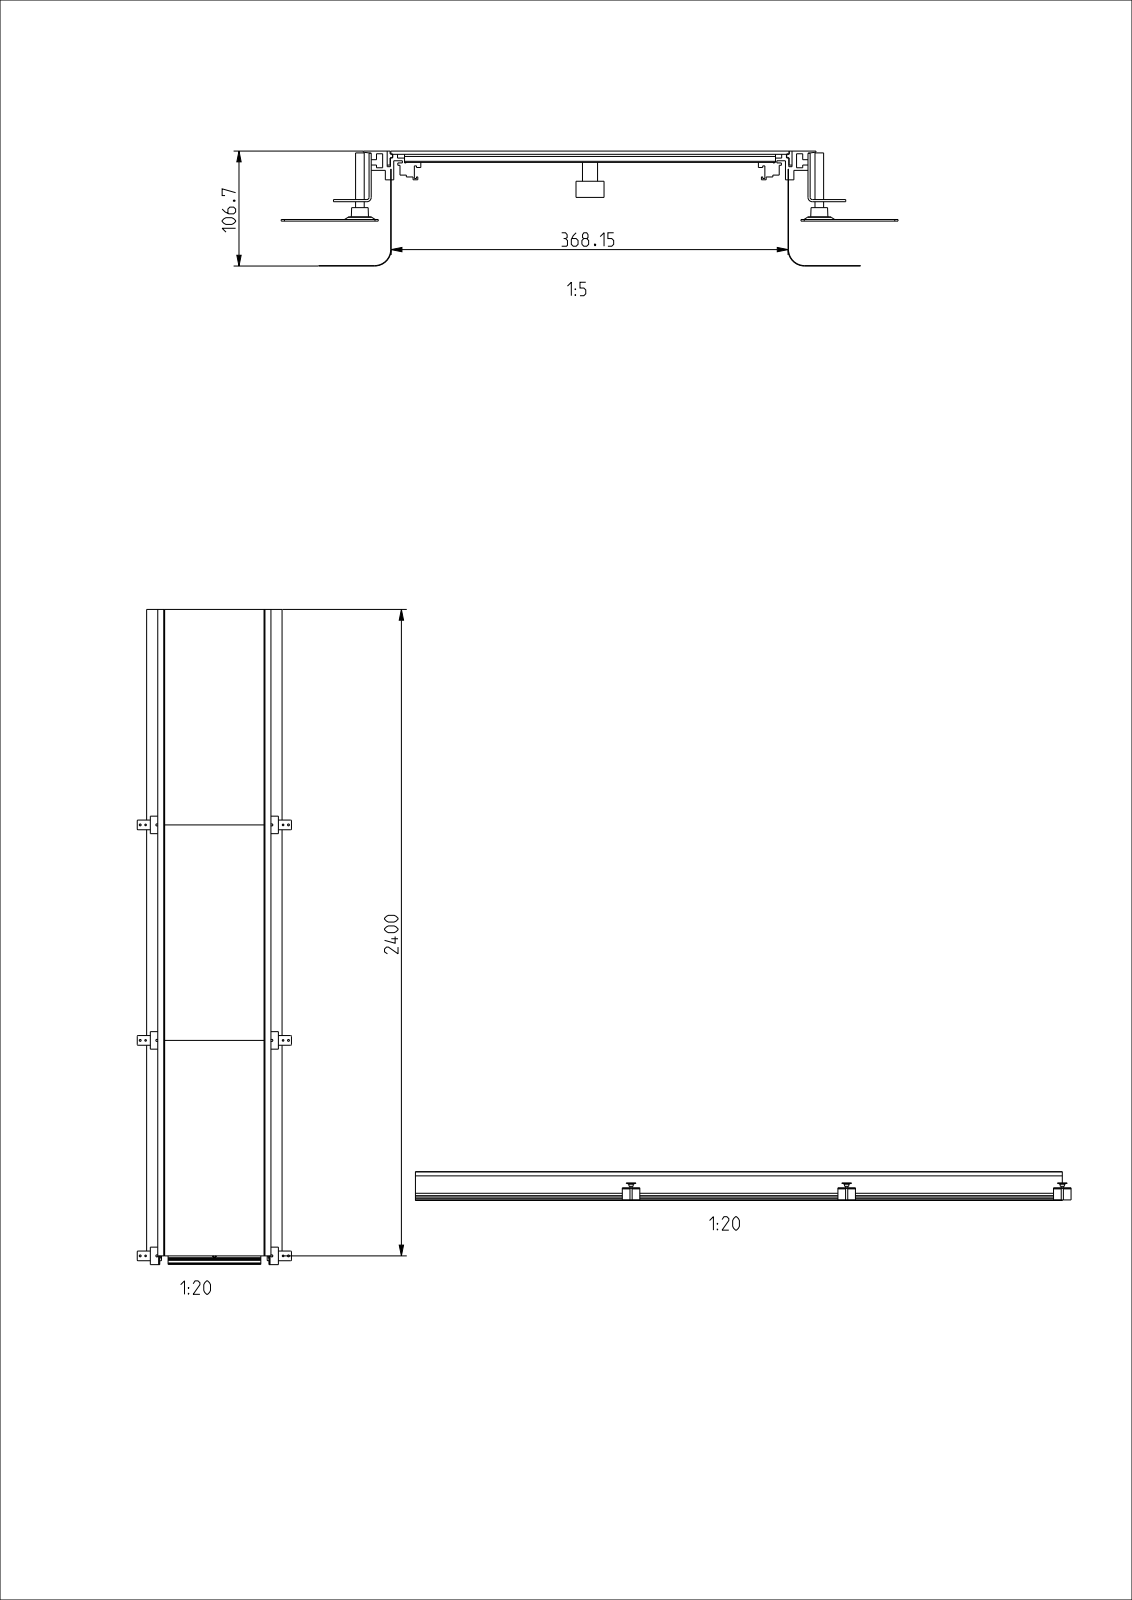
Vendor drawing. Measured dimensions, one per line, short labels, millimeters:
name: U05644KUN; U05650KUN; U05994KUN; U05647KUN (+8 more)
written by: CREO PARAMETRIC BY PTC INC, 2020281 (AUTOMOTIVE_DESIGN)
unit: mm
bodies: 62 solids, 1026 faces (600 planar, 354 cylindrical, 72 other)
size: 2432.5 × 572.13 × 106.7
volume: 6 973 000 mm³; area: 5 476 000 mm²
holes: 15× ⌀7, 9× ⌀8, 9× ⌀10, 6× ⌀6, 6× ⌀8.5, 6× ⌀11.5, 6× ⌀17.5, 6× ⌀23
bosses: 9× ⌀26, 9× ⌀14, 9× ⌀11.9, 6× ⌀20, 6× ⌀8
rounds: 92× R2, 24× R3, 20× R0.5, 2× R4, 2× R15, 2× R15.4
face distances: 3, 0.4, 368.55, 103.7, 106.7, 103.3, 106.3, 6.5, 7.5, 4
hole spacings: 800, 1600, 800.25, 801.1, 802.4, 926.9, 937.16, 959.71
